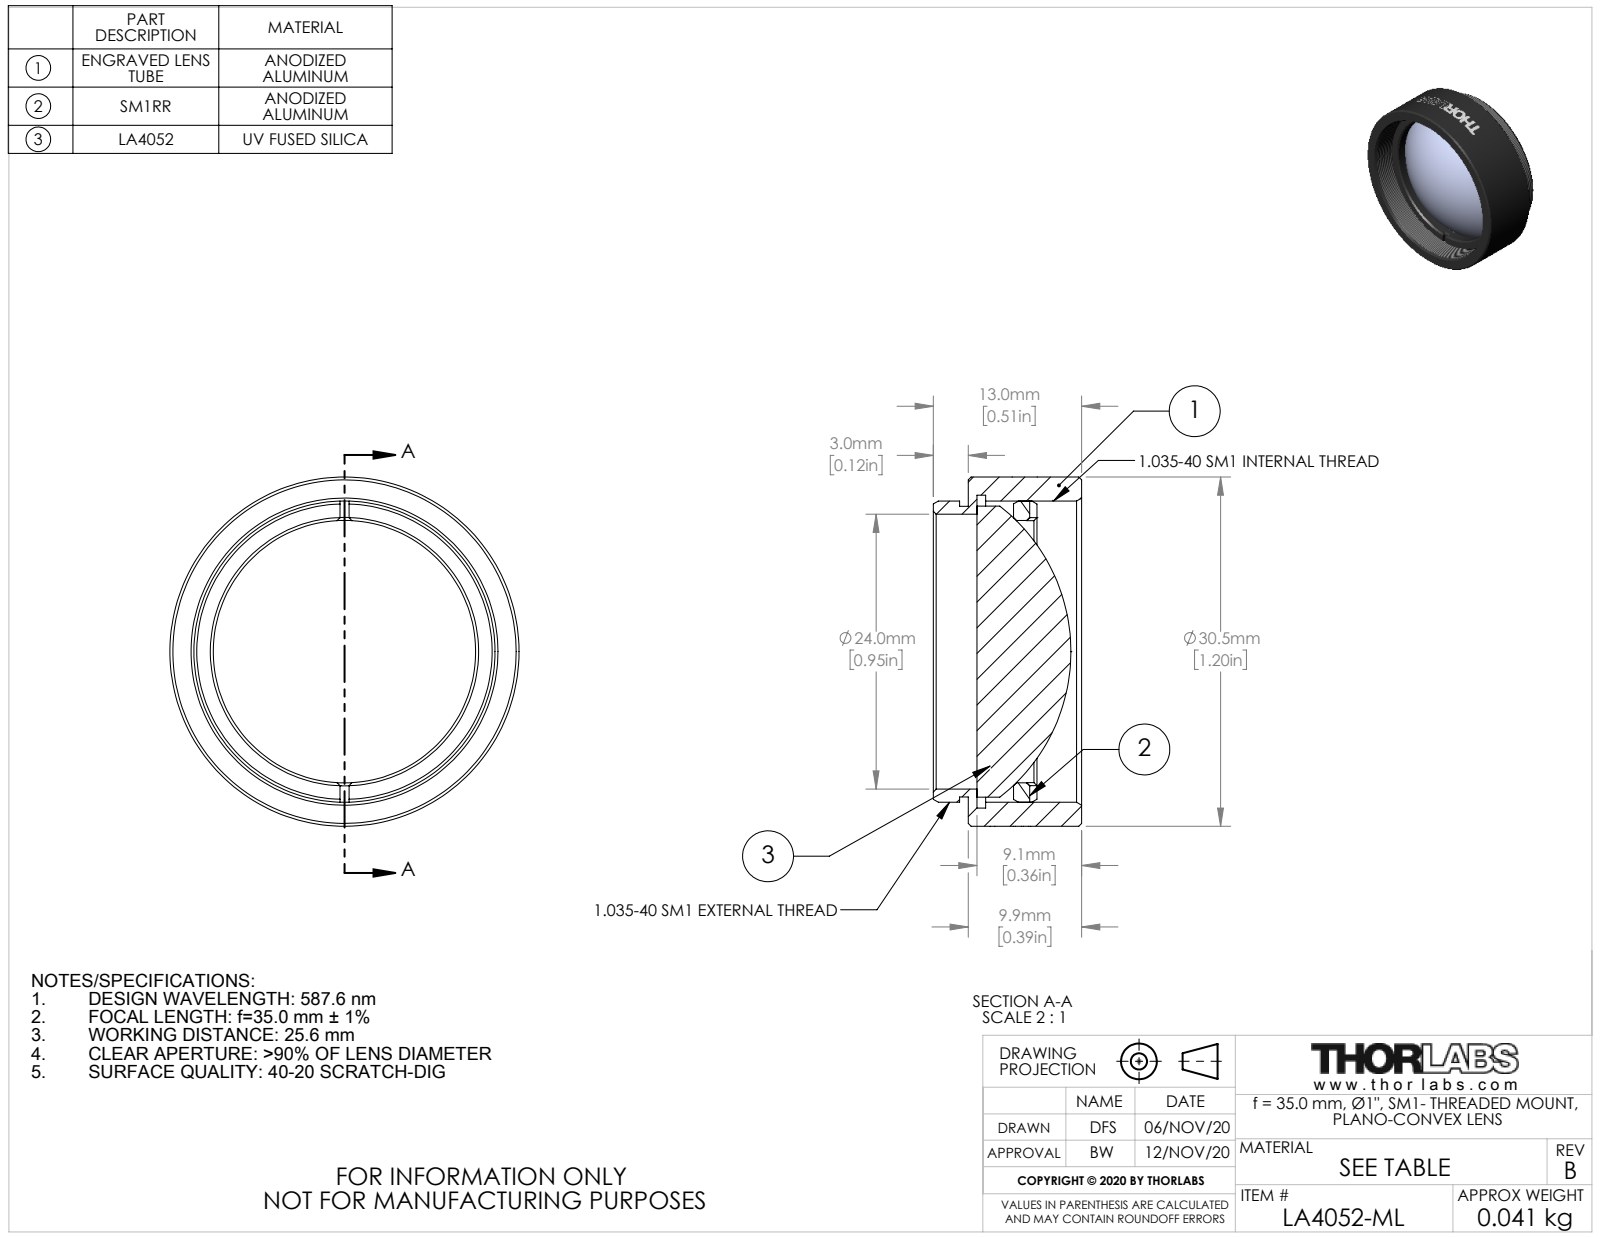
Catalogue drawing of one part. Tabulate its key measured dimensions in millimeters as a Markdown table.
| quantity | value |
| --- | --- |
| part name | 24450-E0W |
| STEP written by | SolidWorks 2018 (CONFIG_CONTROL_DESIGN) |
| units | millimeters |
| bodies | 3 solids, 151 faces (20 planar, 107 cylindrical, 24 other) |
| overall size | 30.48 × 30.48 × 12.95 |
| volume | 5 076 mm³ |
| surface area | 4 705 mm² |
| round holes (diameter × count) | 22.91 × 1, 24 × 1, 27.3 × 1 |
| round bosses / shafts (diameter × count) | 30.48 × 1, 26.29 × 1, 25.4 × 1, 25.37 × 1 |
| main face-to-face distances | 0.77, 9.91, 9.14, 3.97, 3.2, 5.94, 6, 5.23, 2.03, 3.91 |
